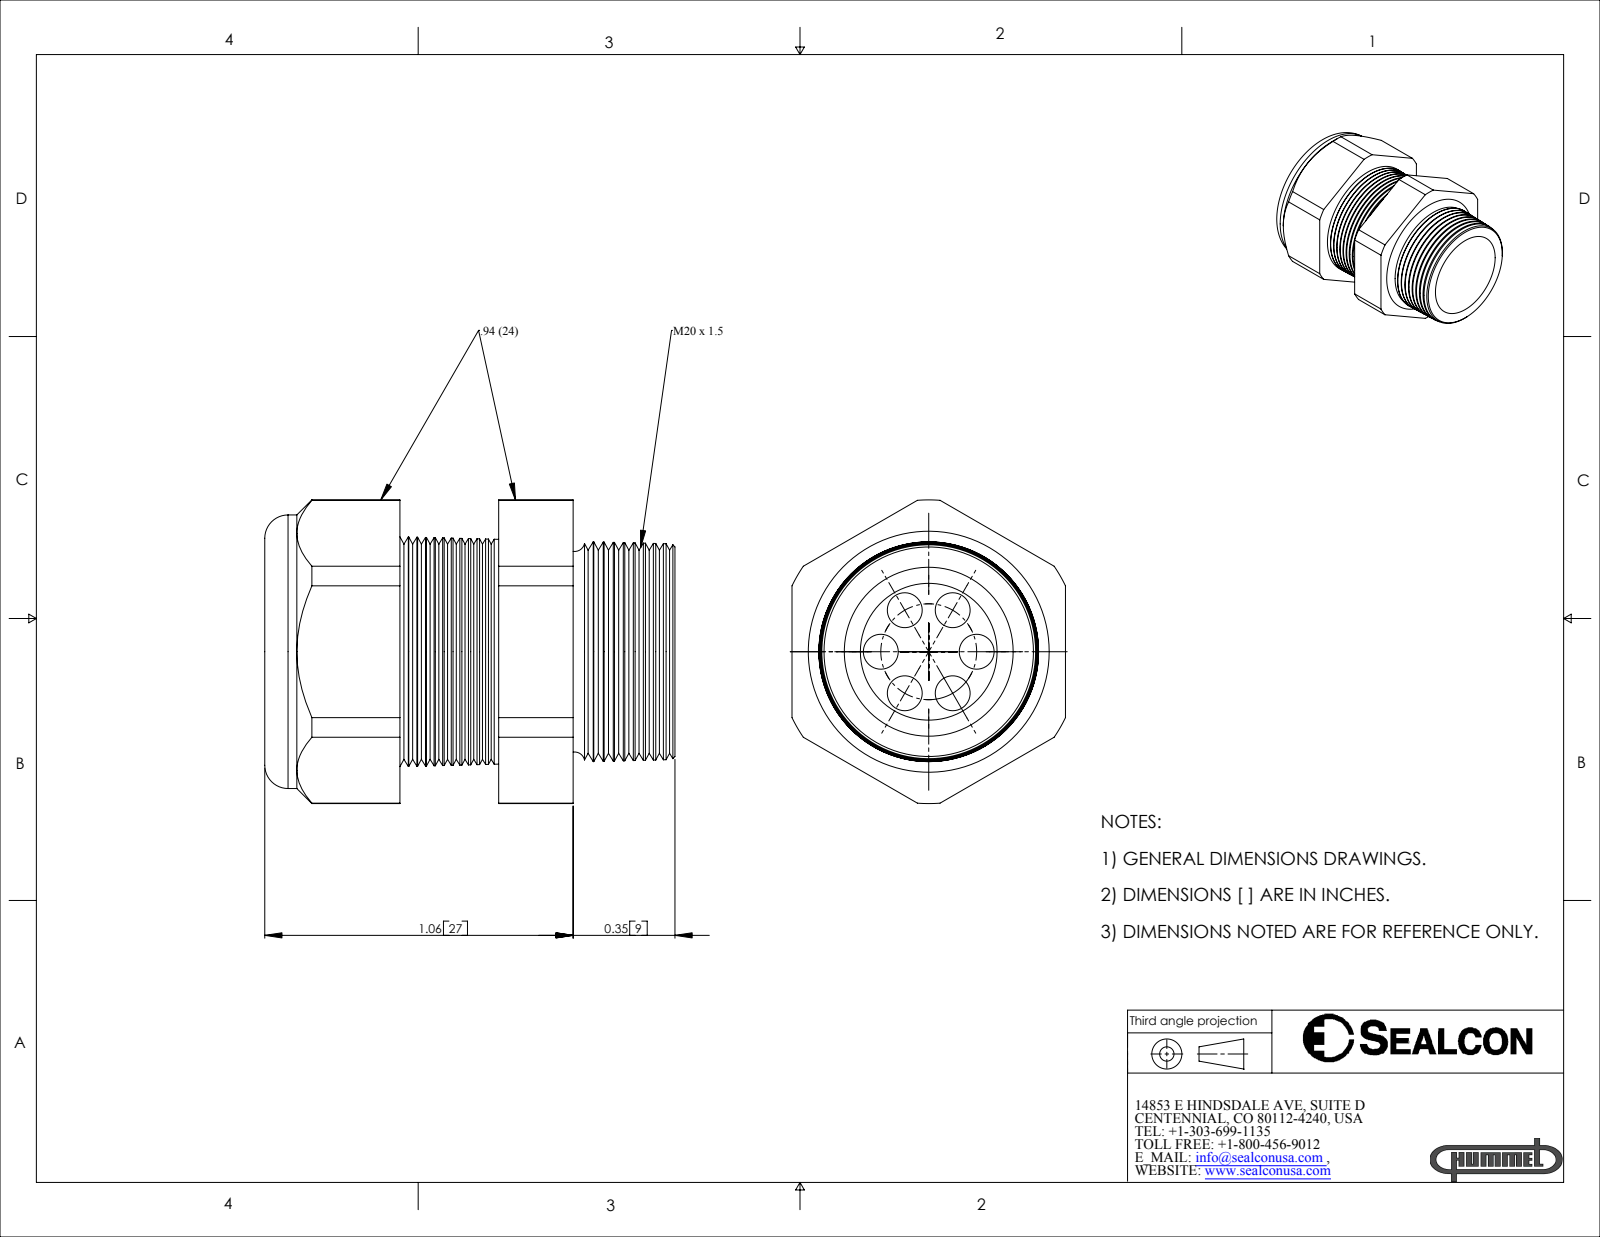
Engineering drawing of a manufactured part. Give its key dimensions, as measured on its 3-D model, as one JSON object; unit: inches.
{"part_name": "CD20M2-GY", "step_written_by": "SolidWorks 2007 (CONFIG_CONTROL_DESIGN)", "units": "inches", "bodies": {"solids": 2, "faces": 186, "planar": 20, "cylindrical": 32, "other": 134}, "overall_size": [1.41, 1.043, 0.94], "volume_in3": 0.57, "surface_area_in2": 10.13, "round_holes": [[0.12, 6], [0.45, 1], [0.47, 1]], "round_bosses_or_shafts": [[0.94, 1]], "partial_cylinders_radius": [[0.522, 1]], "face_to_face_distances": [0.94, 0.804, 0.465, 0.34, 1.06, 0.596, 0.256, 1.41, 0.946, 0.606], "hole_center_spacings": [0.165, 0.285, 0.329]}
